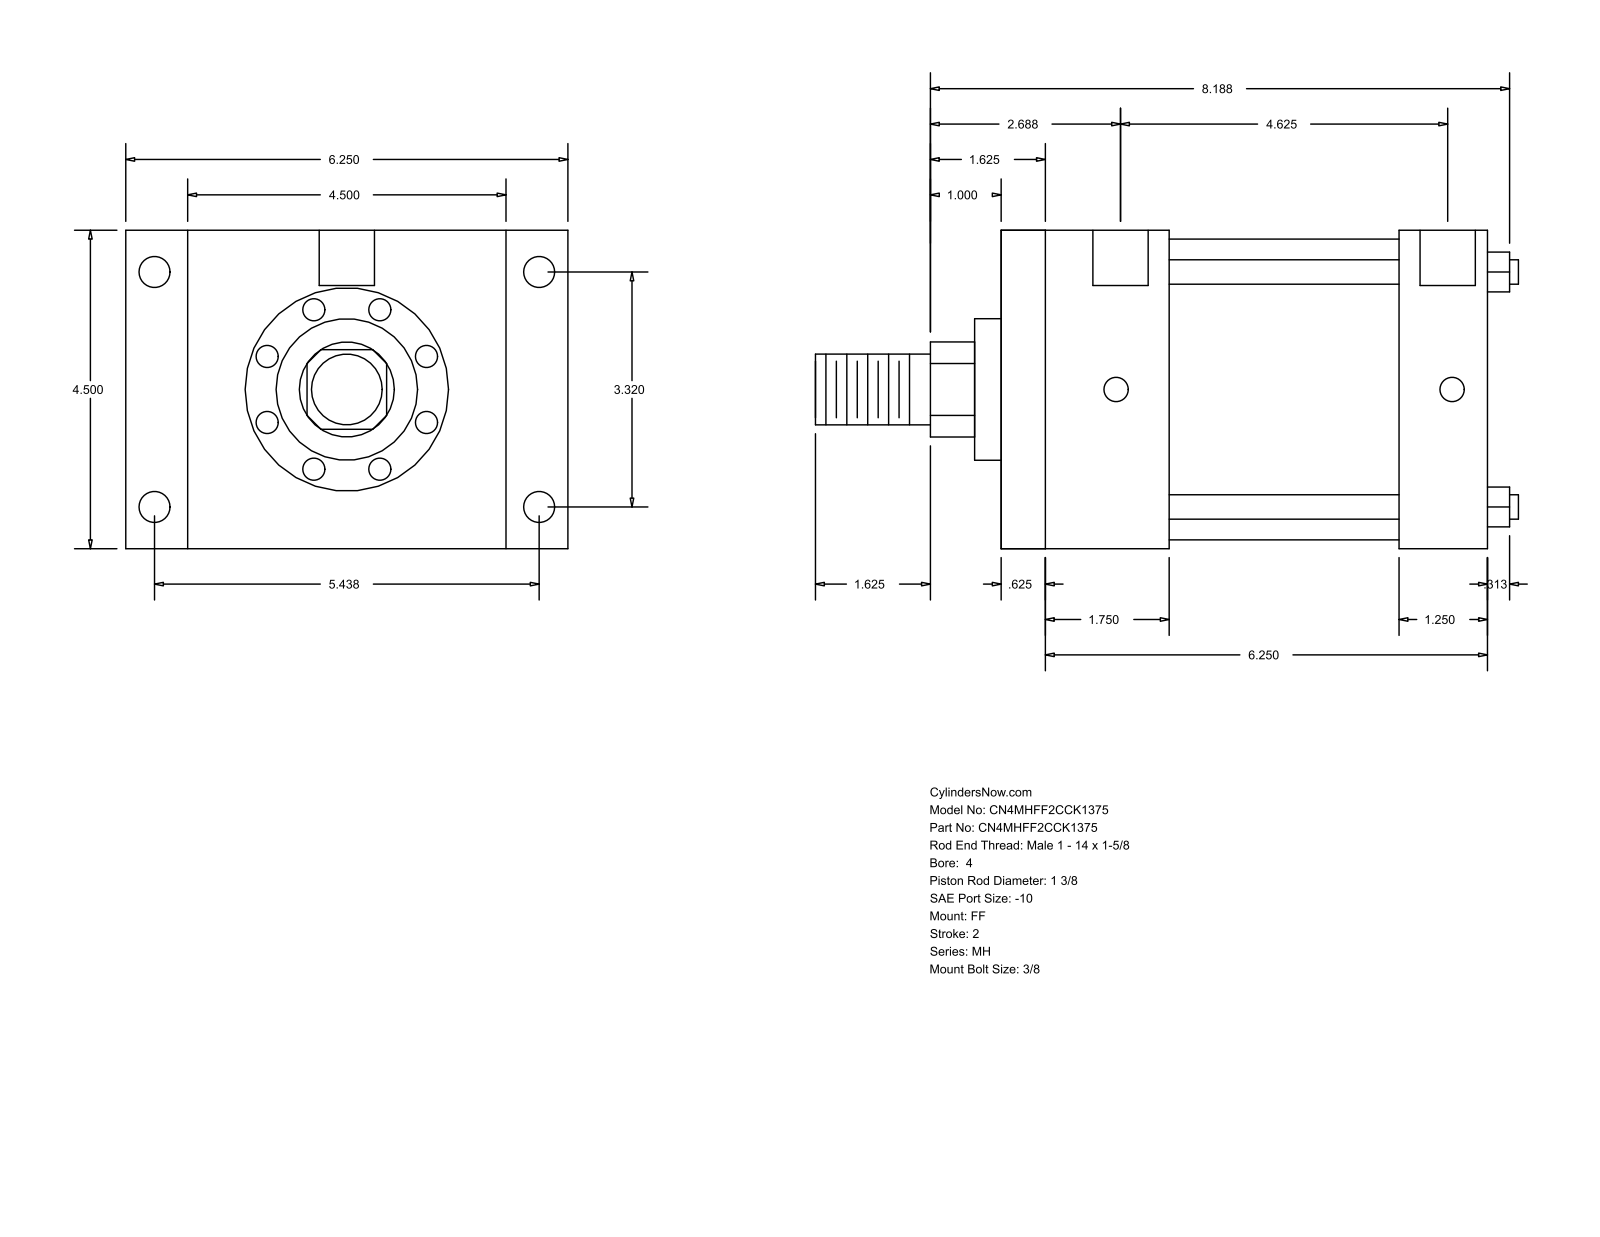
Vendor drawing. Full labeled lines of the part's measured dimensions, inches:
Part name (STEP PRODUCT): MH_FF__0400_1.375
STEP written by: GSSL Pune (CONFIG_CONTROL_DESIGN)
Units: inches
Bodies: 0 solids, 92 faces (64 planar, 28 cylindrical, 0 other)
Overall size (bounding box): 9.937 × 6.25 × 4.5
Round holes (diameter × count): ⌀0.344 ×4, ⌀0.438 ×4, ⌀0.781 ×2
Round bosses / shafts (diameter × count): ⌀0.345 ×4, ⌀4.25 ×1, ⌀2 ×1, ⌀1.375 ×1, ⌀1 ×1
Partial cylindrical surfaces — rounded edges, fillets, slot ends (radius × count): R0.672 ×1
Main face-to-face distances: 4.5, 6.875, 6.25, 0.625, 2.375, 1.75, 4.5, 5.625, 5, 3.25
Hole centre spacings: 3.32, 4.75, 5.438, 6.371, 0.062, 0.063, 4.625, 4.687
